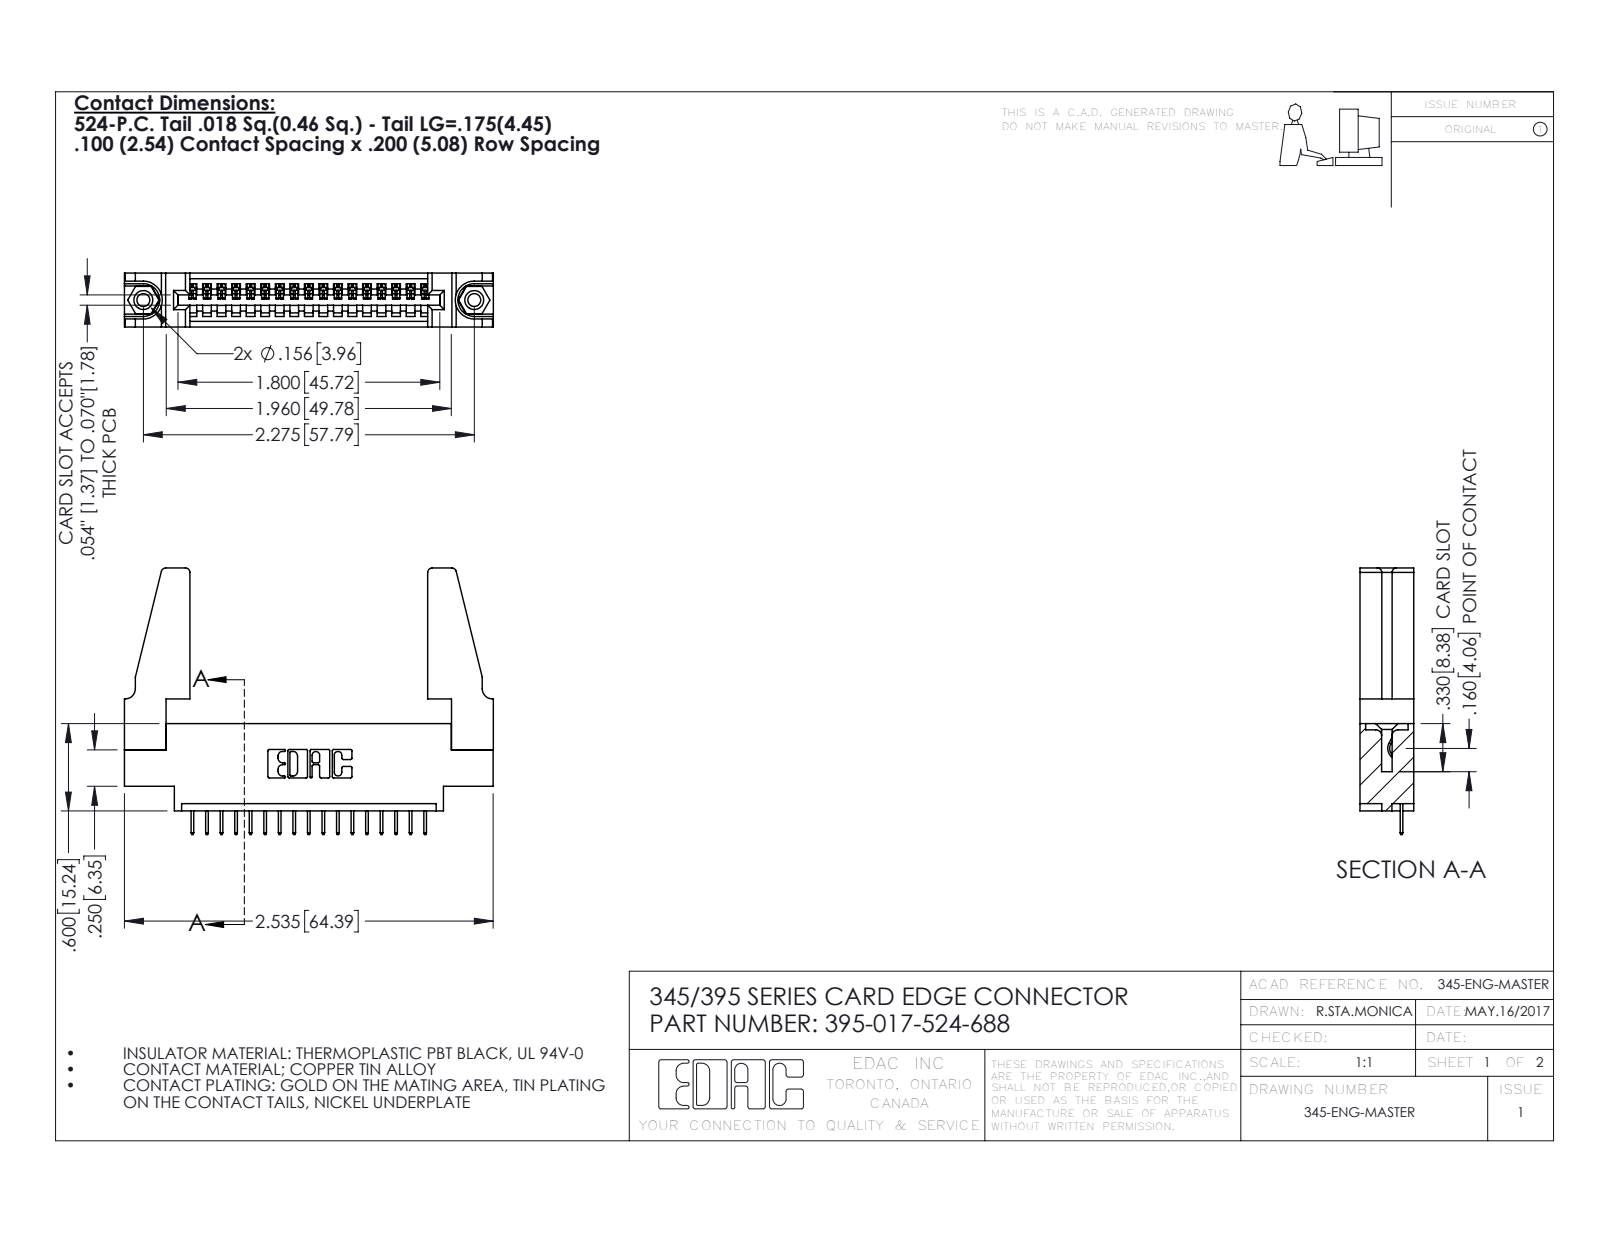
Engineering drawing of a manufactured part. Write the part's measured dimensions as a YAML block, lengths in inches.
part_name: "345-292-001_345-293-124; 345-250-001_345-250-001-102; 345-220-078_345-220-088; 395-017-524-688 (+1 more)"
step_written_by: "SolidWorks 2016 (CONFIG_CONTROL_DESIGN)"
units: inches
bodies: {solids: 22, faces: 1308, planar: 938, cylindrical: 354, other: 16}
overall_size: [2.536, 1.832, 0.37]
volume: 0.548
surface_area: 16
round_holes:
  - {diameter: 0.089, count: 2}
  - {diameter: 0.125, count: 2}
  - {diameter: 0.156, count: 2}
  - {diameter: 0.064, count: 1}
round_bosses_or_shafts:
  - {diameter: 0.155, count: 2}
partial_cylinders:
  - {radius: 0.006, count: 34}
  - {radius: 0.01, count: 22}
  - {radius: 0.03, count: 8}
  - {radius: 0.007, count: 6}
  - {radius: 0.031, count: 6}
  - {radius: 0.026, count: 3}
  - {radius: 0.031, count: 2}
  - {radius: 0.04, count: 2}
face_to_face_distances: [0.37, 0.072, 0.298, 0.2, 0.098, 0.272, 0.025, 0.225, 0.15, 0.148]
hole_center_spacings: [0.27, 2.041, 2.275]
